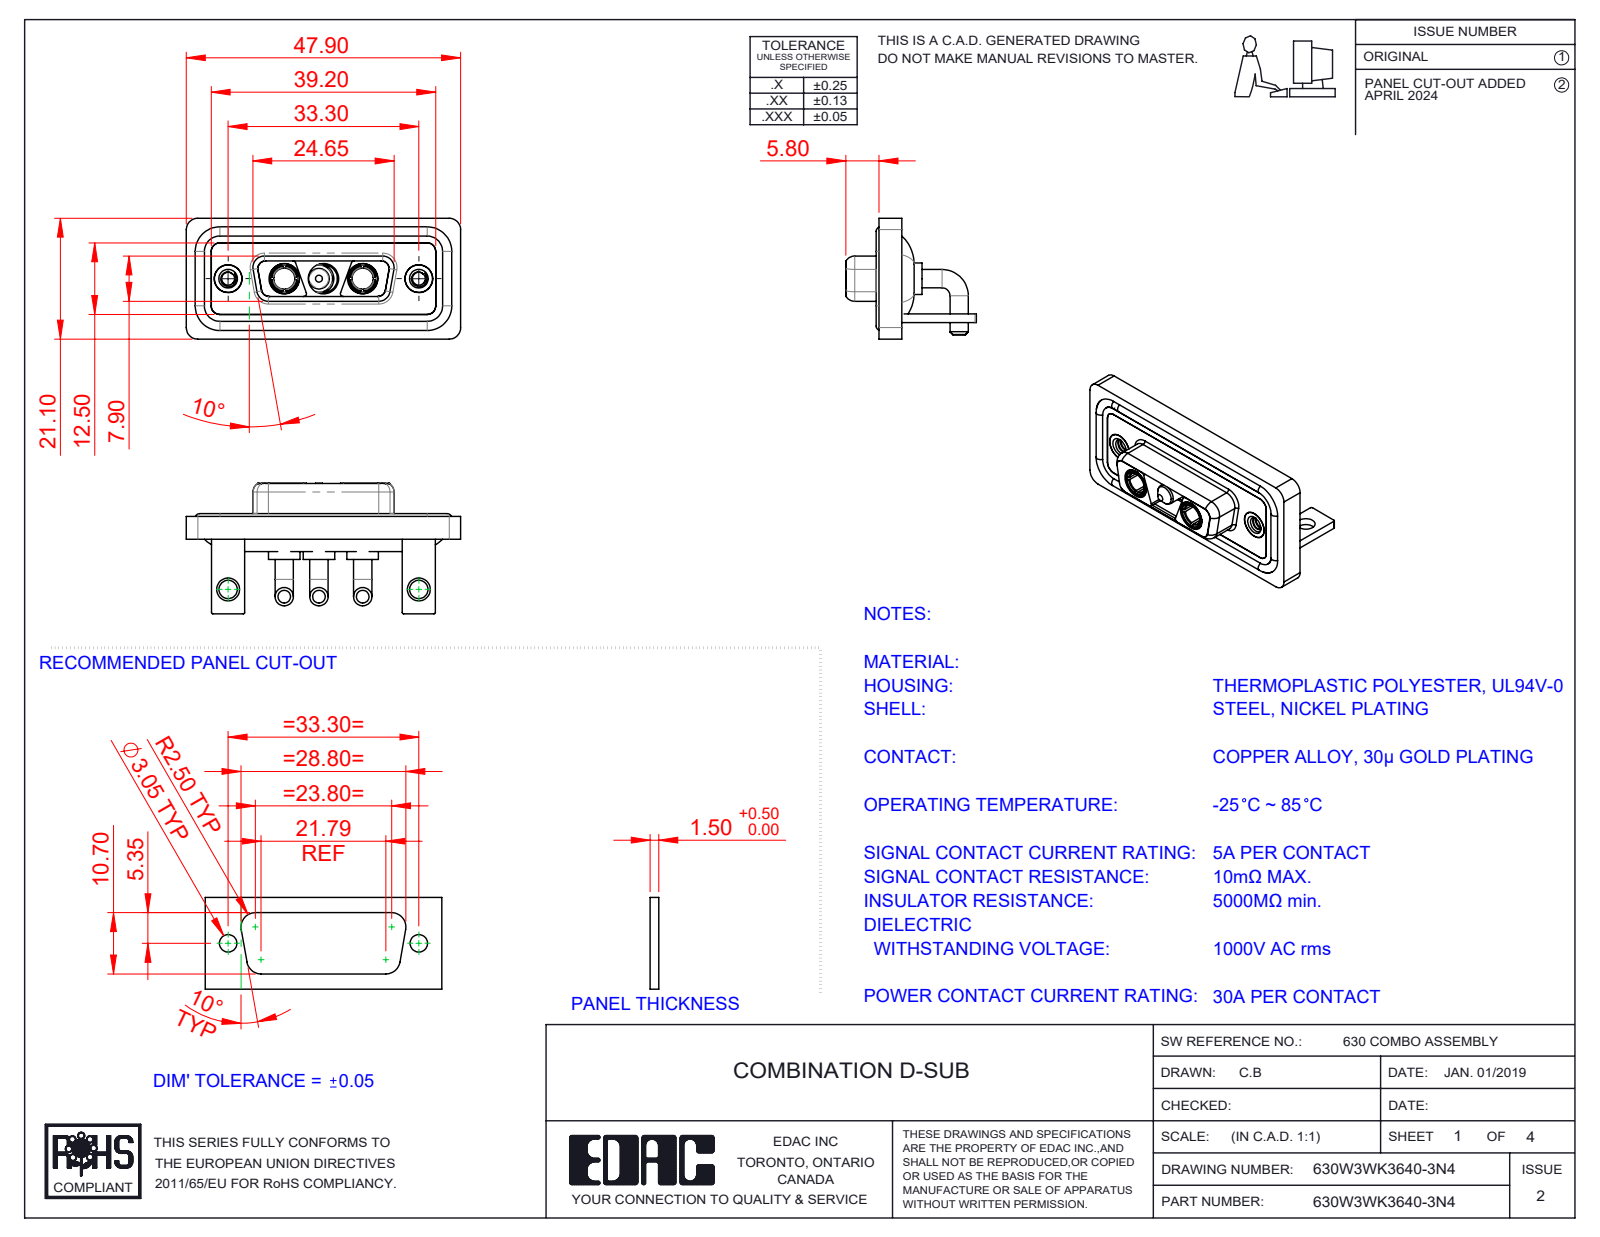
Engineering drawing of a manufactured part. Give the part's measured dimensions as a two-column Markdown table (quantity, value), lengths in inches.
| quantity | value |
| --- | --- |
| part name | 630Combo Stabilizer Bracket_50 Contacts; 630Combo Shell Rear_15 Contacts; Power Socket_30A RA; 630Combo Waterproof Housing_15 Contacts (+5 more) |
| STEP written by | SolidWorks 2023 (CONFIG_CONTROL_DESIGN) |
| units | inches |
| bodies | 15 solids, 643 faces (198 planar, 288 cylindrical, 157 other) |
| overall size | 1.886 × 0.898 × 0.831 |
| volume | 0.396 in³ |
| surface area | 16.32 in² |
| round holes (diameter × count) | 0.191 × 5, 0.209 × 3, 0.089 × 2, 0.126 × 2, 0.146 × 2, 0.157 × 2, 0.159 × 2, 0.197 × 2 |
| round bosses / shafts (diameter × count) | 0.126 × 6, 0.063 × 4, 0.217 × 3, 0.205 × 3, 0.187 × 3, 0.148 × 3, 0.195 × 2, 0.195 × 2 |
| partial cylindrical surfaces (radius × count) | 0.079 × 21, 0.059 × 18, 0.01 × 16, 0.053 × 12, 0.02 × 9, 0.063 × 8, 0.024 × 4, 0.026 × 4 |
| main face-to-face distances | 0.016, 0.114, 0.059, 0.146, 0.071, 0.043, 0.161, 0.063, 0.098, 0.055 |
| hole center spacings | 0.27, 0.386, 0.656, 0.925, 1.311, 0.539 |
